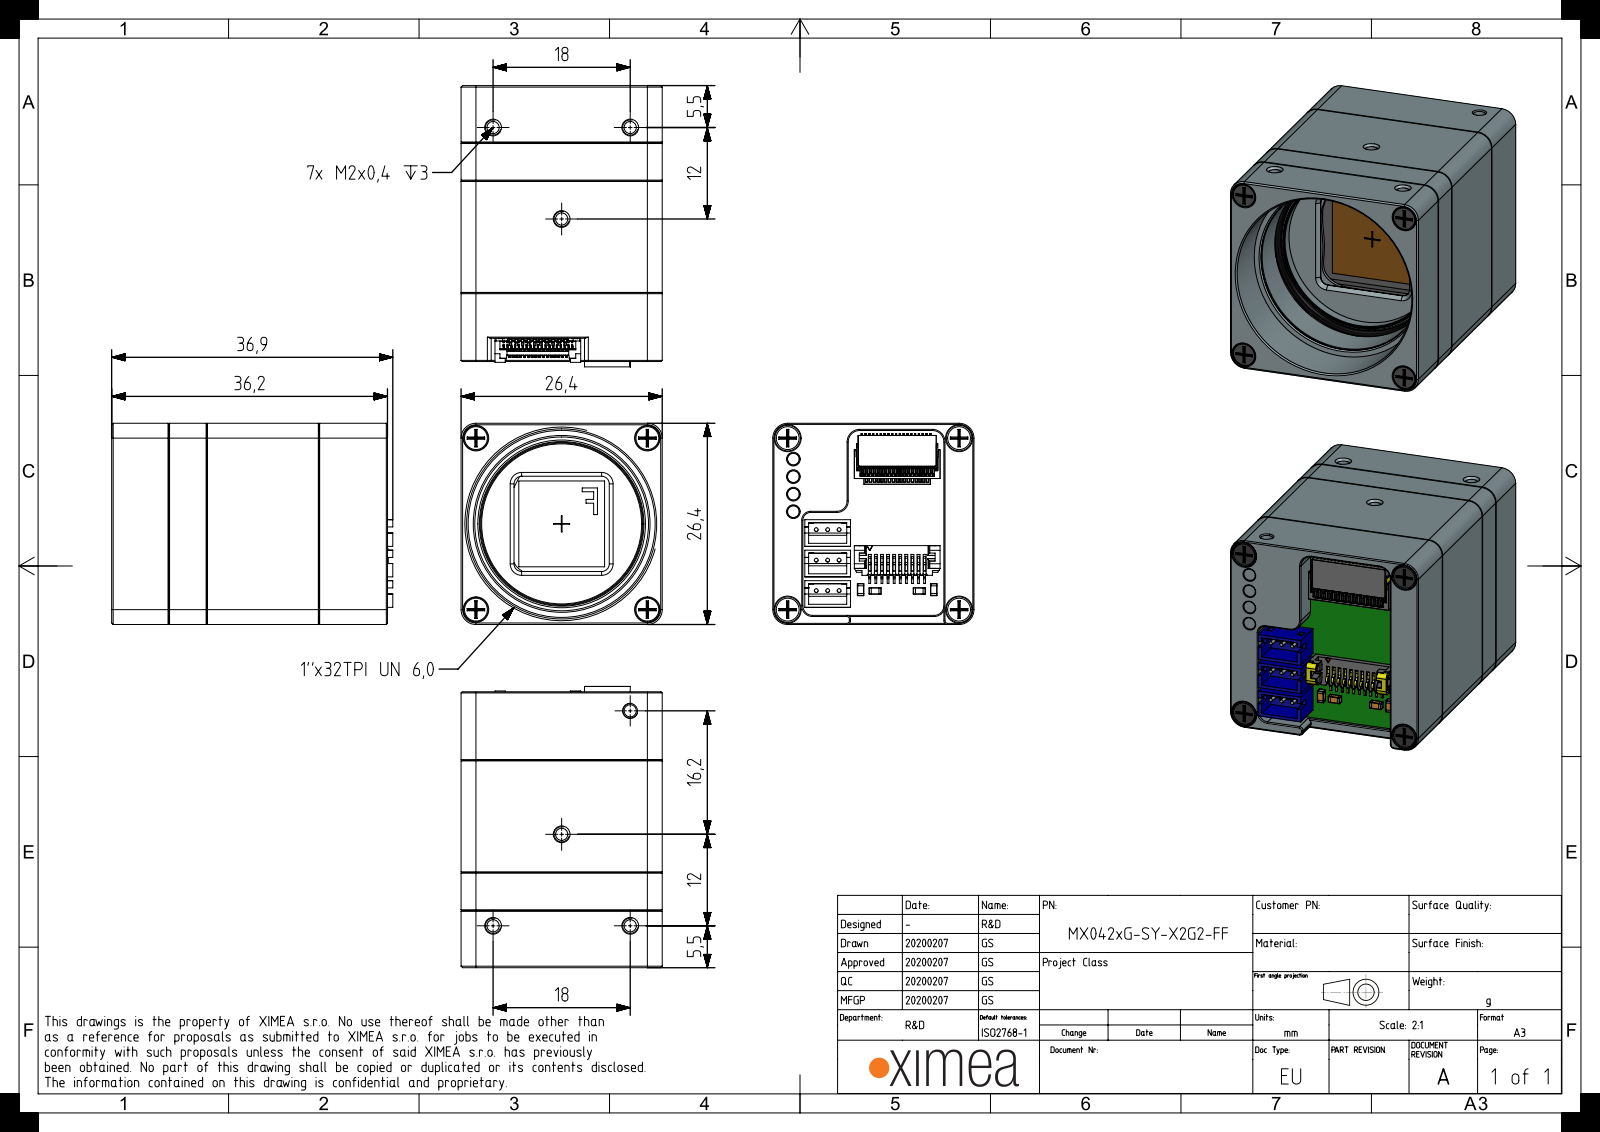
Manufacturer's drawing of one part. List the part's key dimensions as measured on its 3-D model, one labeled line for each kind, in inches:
Part name (STEP PRODUCT): CMV4000_Glass; CMV4000_Package; ANDON-96UPGA-Socket; MX-X2G2-MAIN-FF-PCA-REV2 (+8 more)
STEP written by: SIEMENS PLM Software NX 1907 (AUTOMOTIVE_DESIGN)
Units: inches
Bodies: 427 solids, 15297 faces (9438 planar, 4500 cylindrical, 1359 other)
Overall size (bounding box): 1.453 × 1.039 × 1.039
Volume: 0.732 in³ · Surface area: 40.23 in²
Round holes (diameter × count): ⌀0.02 ×95, ⌀0.03 ×95, ⌀0.063 ×16, ⌀0.028 ×9, ⌀0.079 ×8, ⌀0.035 ×4, ⌀0.035 ×4, ⌀0.071 ×4, ⌀0.083 ×4, ⌀0.118 ×4, ⌀0.126 ×4, ⌀0.132 ×4
Round bosses / shafts (diameter × count): ⌀0.012 ×95, ⌀0.02 ×9, ⌀0.075 ×8, ⌀0.118 ×6, ⌀0.064 ×4, ⌀0.033 ×4, ⌀0.063 ×2, ⌀0.031 ×2
Partial cylindrical surfaces — rounded edges, fillets, slot ends (radius × count): R0.006 ×92, R0.004 ×85, R0.013 ×28, R0.015 ×27, R0.039 ×24, R0.059 ×20, R0.012 ×17, R0.051 ×16
Main face-to-face distances: 1.039, 0.039, 0.142, 0.181, 0.622, 0.807, 0.185, 0.319, 0.177, 0.224
Hole centre spacings: 0.112, 0.25, 0.158, 0.269, 0.18, 0.206, 0.354, 0.212
